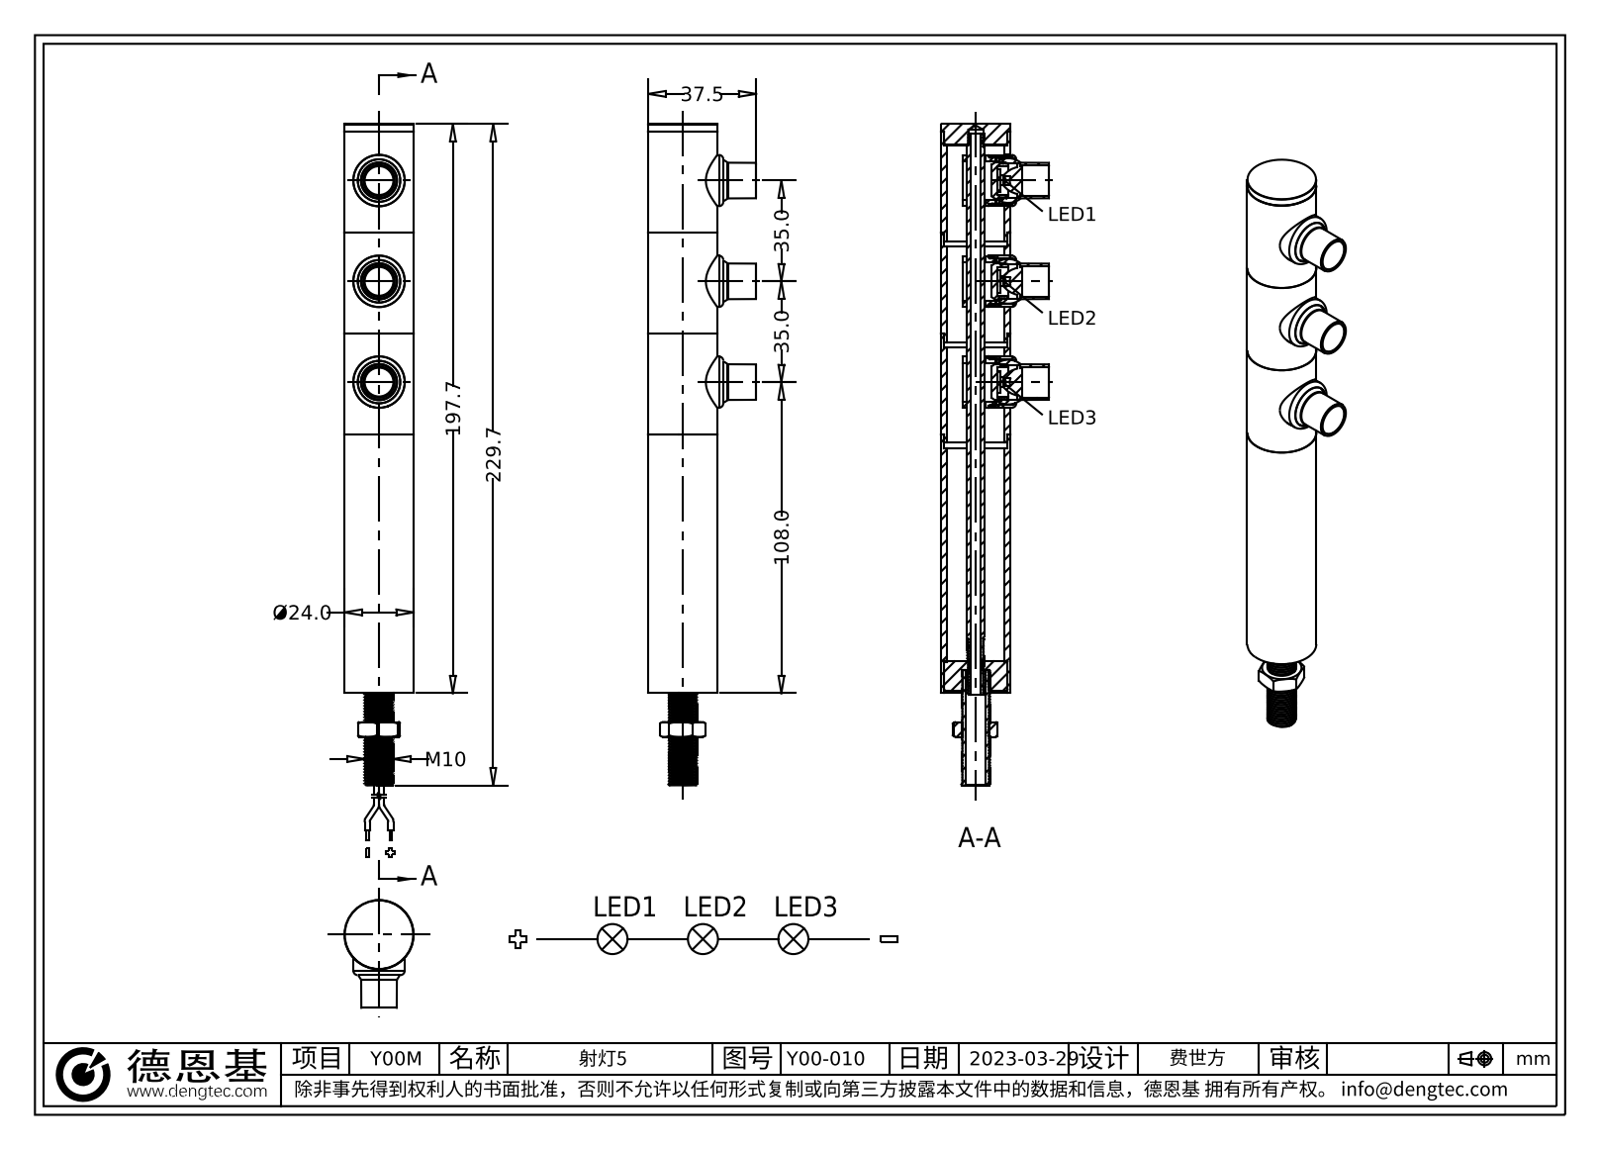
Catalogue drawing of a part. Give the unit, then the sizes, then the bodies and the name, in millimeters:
Units: millimetres
Overall size (bounding box): 229.7 × 37.44 × 28.99
Round holes (diameter × count): ⌀2 ×6, ⌀3 ×3, ⌀10.1 ×3, ⌀10.6 ×3, ⌀12 ×3, ⌀12.7 ×3, ⌀13.4 ×3, ⌀14.7 ×3, ⌀15.9 ×3, ⌀17.9 ×3, ⌀3.4 ×1, ⌀5 ×1
Round bosses / shafts (diameter × count): ⌀10 ×4, ⌀17.8 ×3, ⌀17.7 ×3, ⌀16.5 ×3, ⌀13.1 ×3, ⌀12.6 ×3, ⌀24 ×1, ⌀22 ×1
Partial cylindrical surfaces — rounded edges, fillets, slot ends (radius × count): R2 ×6, R3.9 ×3, R1.65 ×2
Main face-to-face distances: 35, 70, 1, 2.9, 186.4, 4.8, 11.8, 179.2, 7.2, 10.3
Hole centre spacings: 35, 35.17, 35.18, 70.09, 70, 3.51, 3.49, 35.69
Volume: 45 027 mm³ · Surface area: 57 309 mm²
Bodies: 33 solids, 703 faces (161 planar, 369 cylindrical, 173 other)
Part name (STEP PRODUCT): 灯组件; 中心连接杆; 转动固定盖; 灯罩本体底座 (+8 more)
STEP written by: SolidWorks 2018 (CONFIG_CONTROL_DESIGN)
